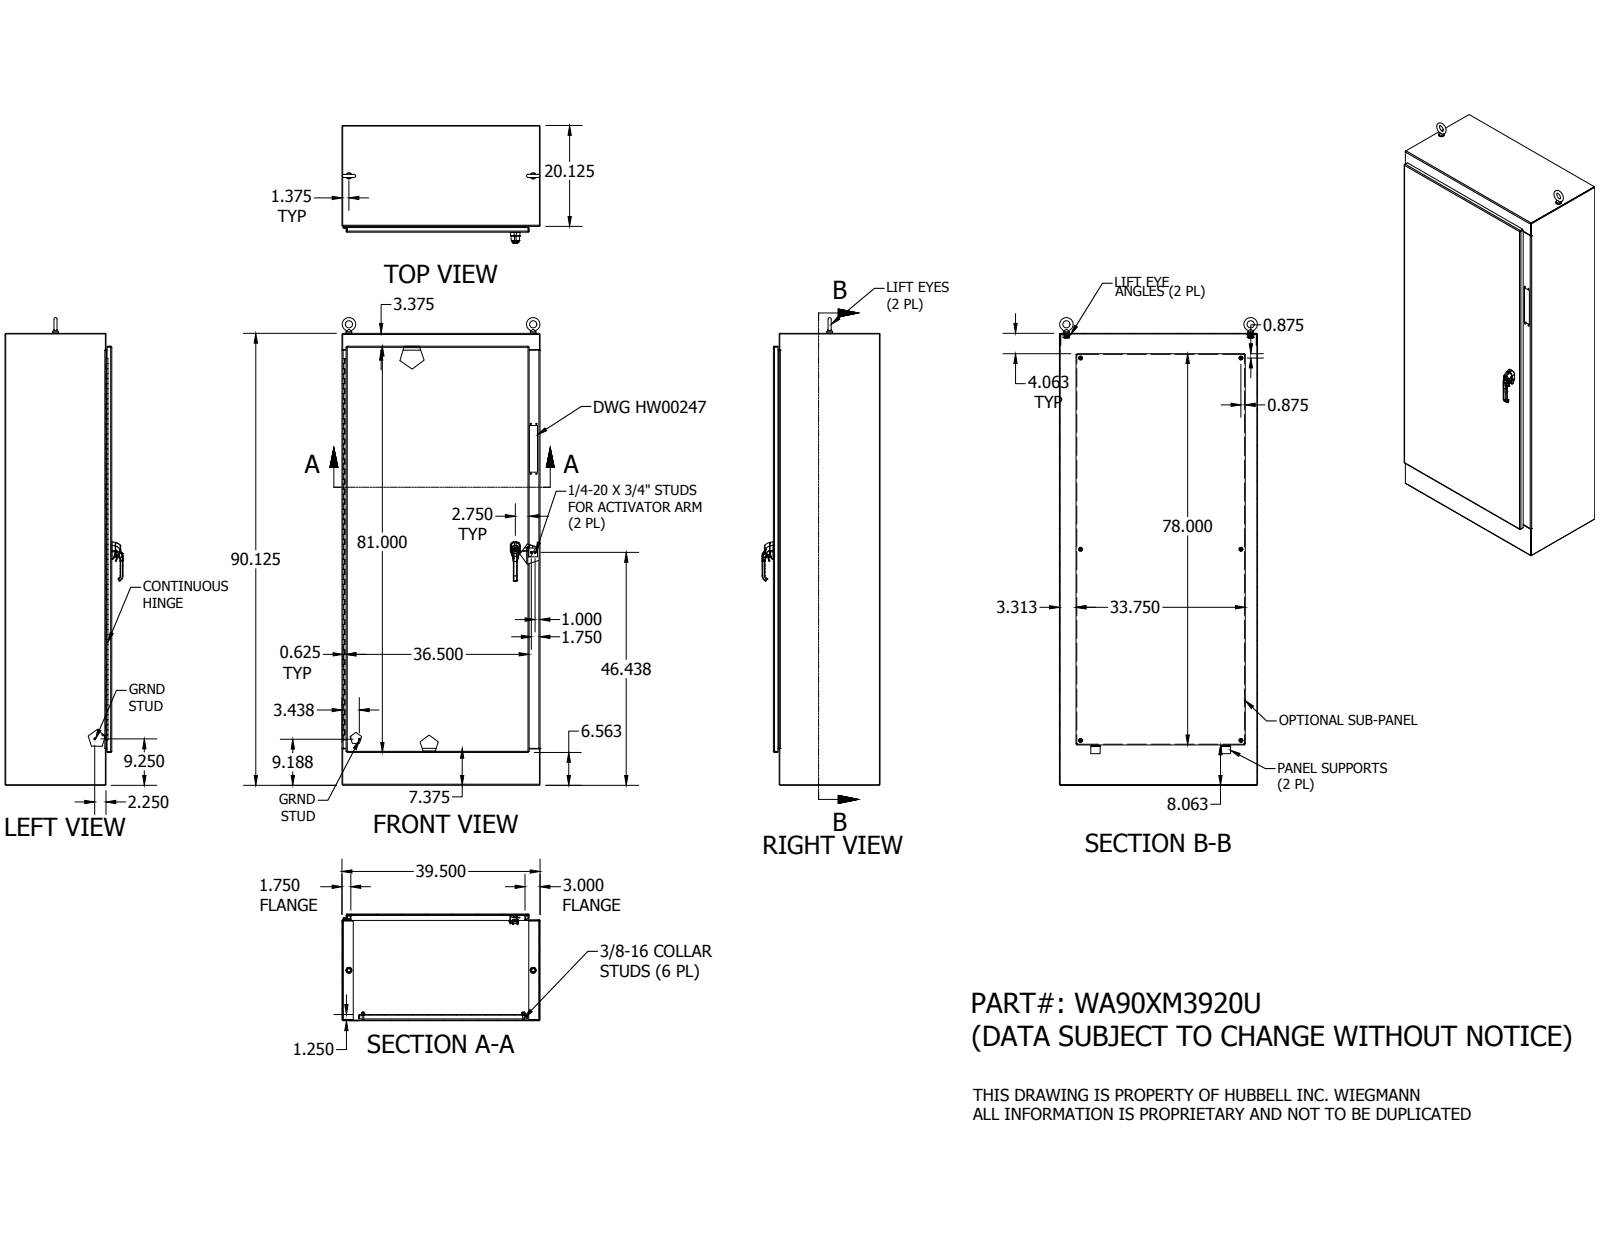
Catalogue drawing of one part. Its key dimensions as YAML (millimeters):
part_name: "WA90XM39U_BACK; WA90XM20U_RIGHT_SIDE; WA90XM20U_LEFT_SIDE; WAXM3920U_TOP_ENDWALL (+8 more)"
step_written_by: "Autodesk Inventor 2014 (AUTOMOTIVE_DESIGN)"
units: millimeters
bodies: {solids: 103, faces: 3815, planar: 1696, cylindrical: 1268, other: 851}
overall_size: [2368.49, 1003.3, 597.94]
volume: 33040000
surface_area: 21150000
round_holes:
  - {diameter: 9.52, count: 10}
  - {diameter: 7.02, count: 8}
  - {diameter: 7.14, count: 7}
  - {diameter: 3.96, count: 6}
  - {diameter: 6.35, count: 6}
  - {diameter: 7.8, count: 6}
  - {diameter: 14.29, count: 6}
  - {diameter: 5.08, count: 4}
  - {diameter: 7.37, count: 4}
  - {diameter: 5.4, count: 3}
  - {diameter: 3, count: 2}
  - {diameter: 3.17, count: 2}
round_bosses_or_shafts:
  - {diameter: 15.88, count: 10}
  - {diameter: 8.38, count: 9}
  - {diameter: 14.29, count: 6}
  - {diameter: 9.52, count: 4}
  - {diameter: 8.56, count: 4}
  - {diameter: 6.35, count: 4}
  - {diameter: 6, count: 3}
  - {diameter: 31.75, count: 2}
partial_cylinders:
  - {radius: 0.5, count: 187}
  - {radius: 0.3, count: 109}
  - {radius: 0.51, count: 48}
  - {radius: 0.47, count: 21}
  - {radius: 2.38, count: 21}
  - {radius: 5.56, count: 20}
  - {radius: 1.27, count: 14}
  - {radius: 2, count: 14}
face_to_face_distances: [3.17, 3.18, 28.58, 537.64, 534.47, 540.82, 537.65, 31.75, 505.89, 509.07]
hole_center_spacings: [771.85, 812.8, 9.67, 9.69, 9.72, 19.05, 19.36, 19.4]
